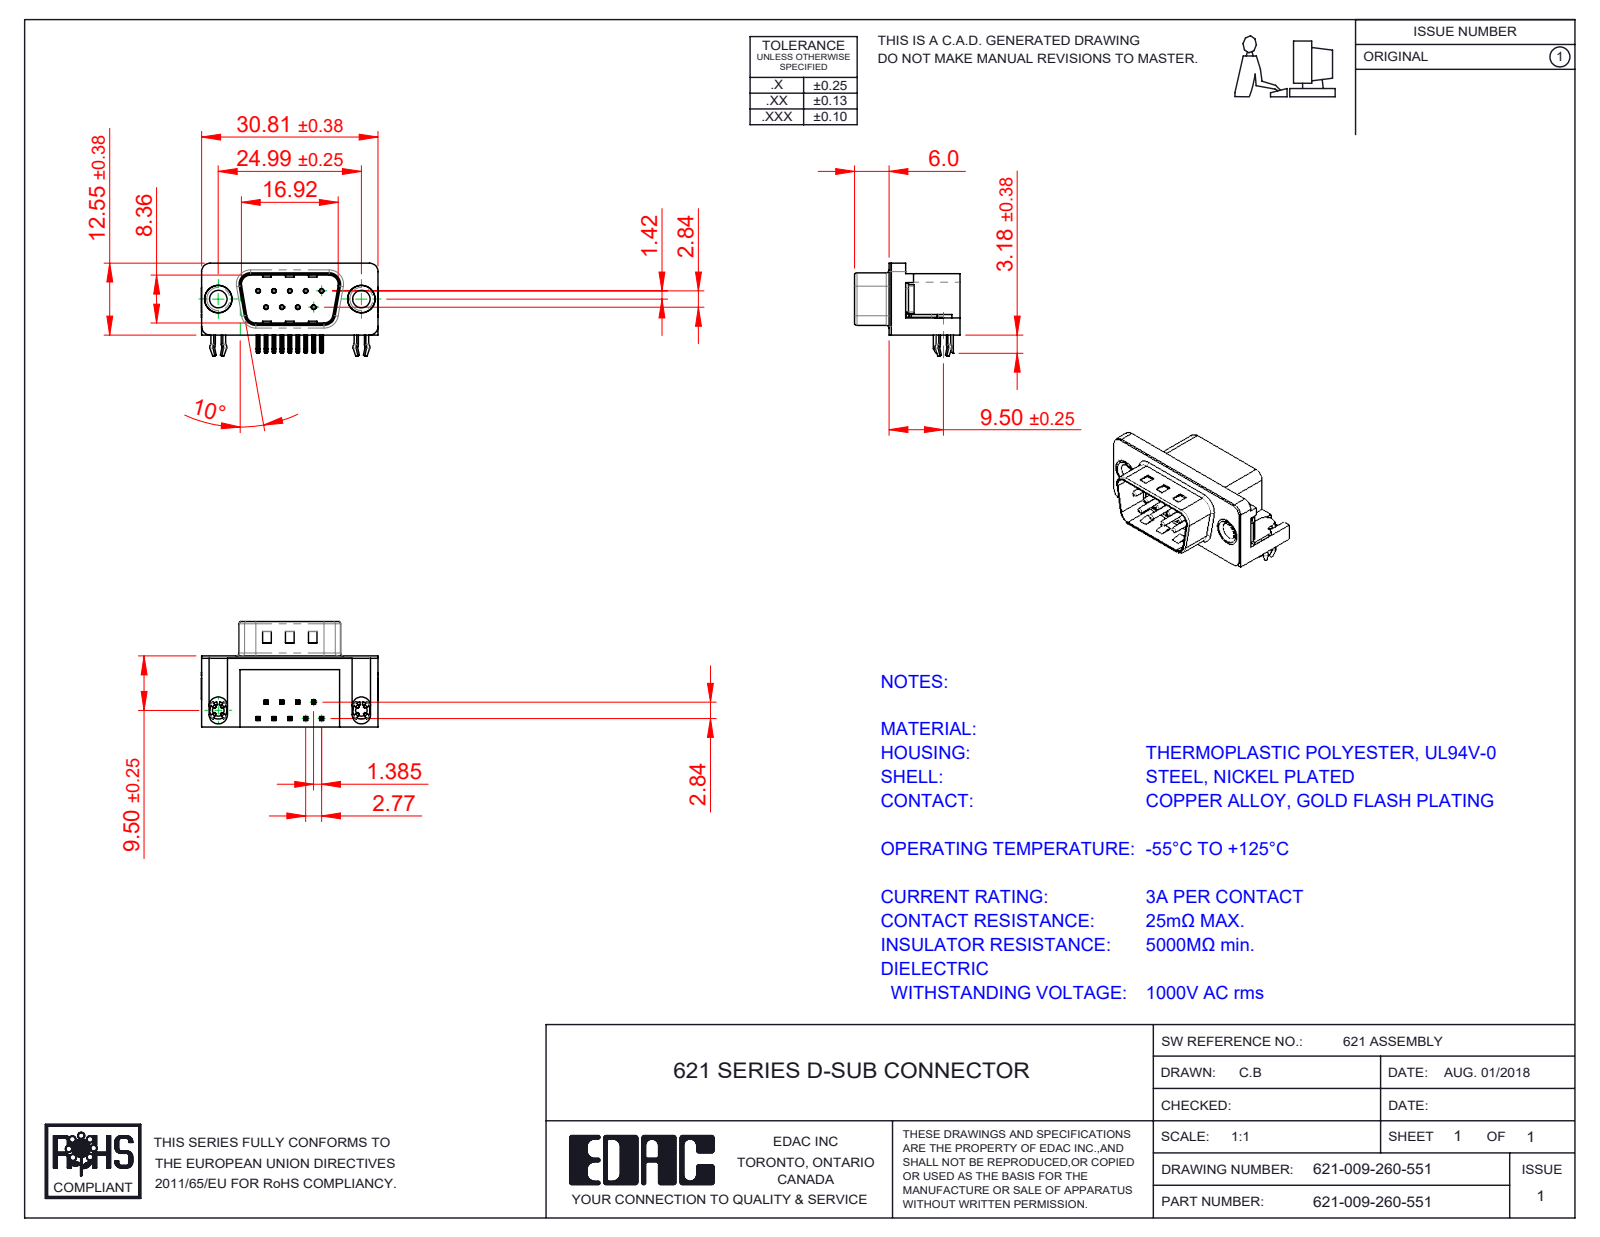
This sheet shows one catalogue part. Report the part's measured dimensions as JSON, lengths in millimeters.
{"part_name": "621 Shell_9 Socket; 621 Thru Hole Rivet; 621 Contact Top; 621-009-260-551 (+3 more)", "step_written_by": "SolidWorks 2016 (CONFIG_CONTROL_DESIGN)", "units": "millimeters", "bodies": {"solids": 15, "faces": 981, "planar": 573, "cylindrical": 309, "other": 99}, "overall_size": [30.89, 18.4, 15.73], "volume_mm3": 3245, "surface_area_mm2": 4477, "round_holes": [[0.35, 9], [0.8, 9], [2.26, 2], [3.05, 2], [4, 2], [4.8, 2], [5, 2]], "round_bosses_or_shafts": [[0.75, 9], [4.9, 2], [4.75, 2], [3.85, 2], [3.26, 2]], "partial_cylinders_radius": [[0.25, 44], [0.12, 18], [1, 16], [0.5, 9], [1.5, 8], [1.6, 8], [0.9, 4], [2, 4]], "face_to_face_distances": [0.4, 12, 12.4, 10.35, 2.9, 9.5, 2.5, 0.5, 2.1, 0.35], "hole_center_spacings": [3.16, 2.77, 5.54, 5.03, 5.04, 8.31, 7.48, 7.49]}
